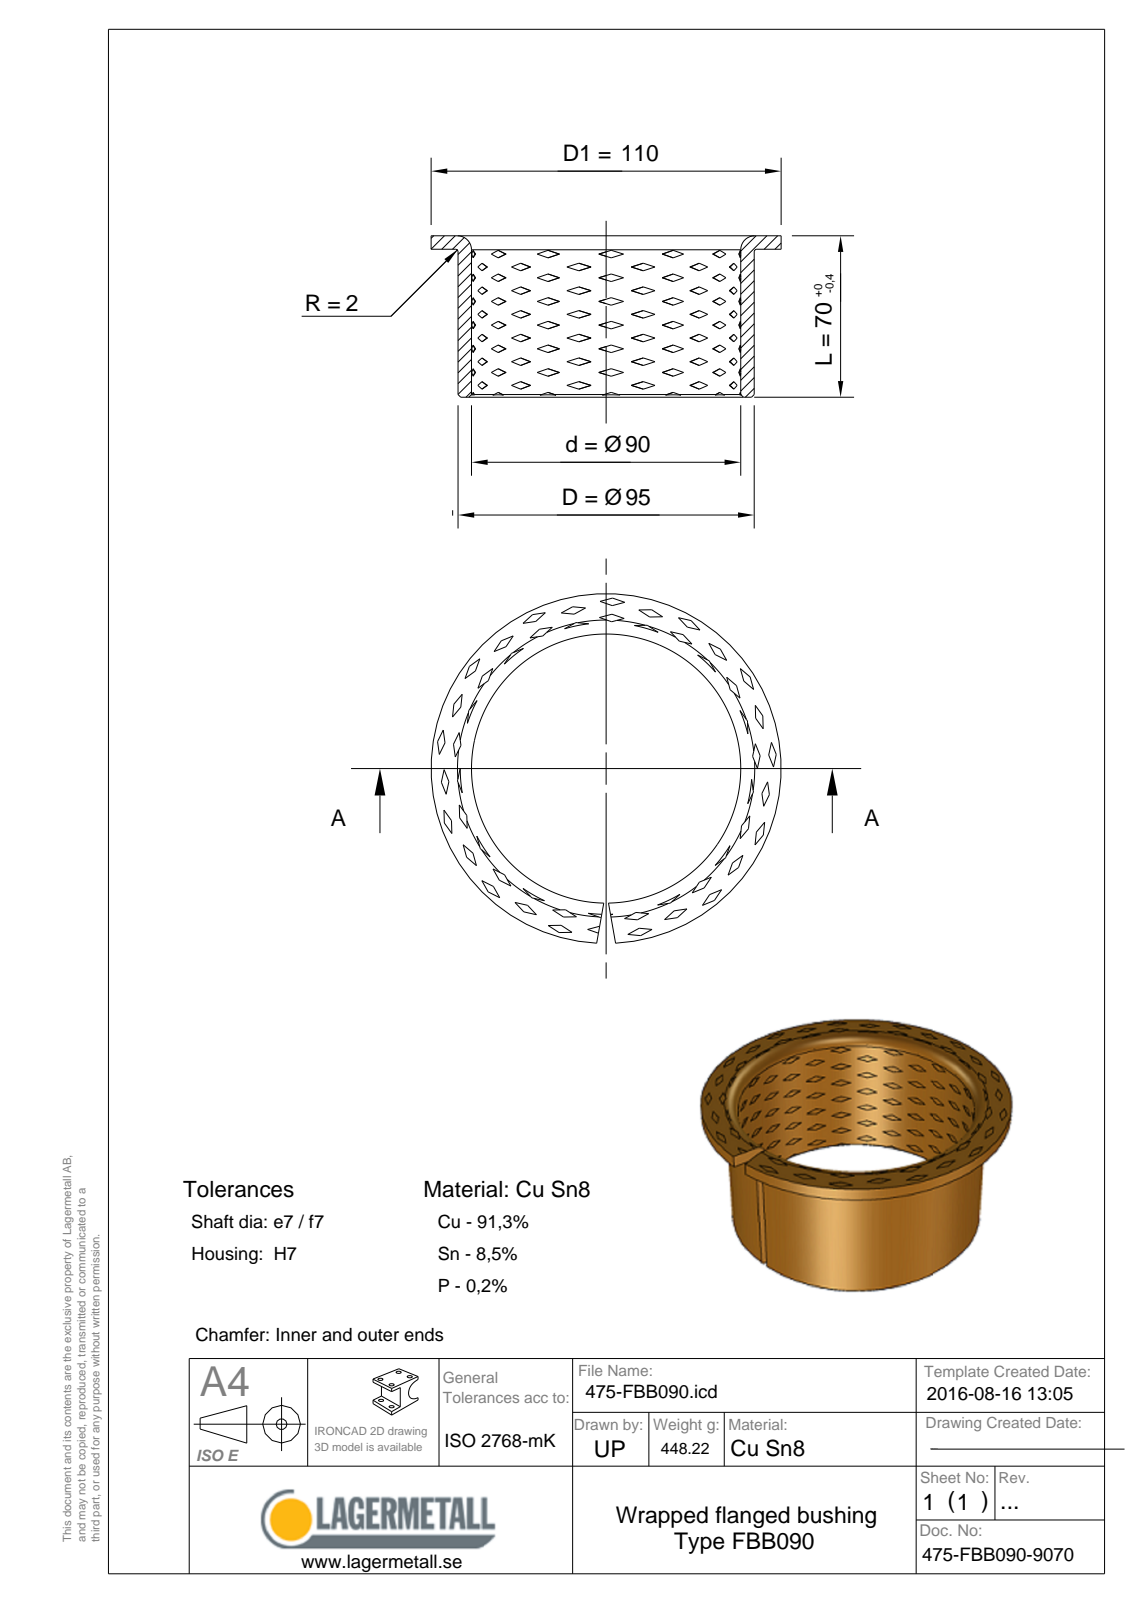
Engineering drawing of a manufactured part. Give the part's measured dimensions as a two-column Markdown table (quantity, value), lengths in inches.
| quantity | value |
| --- | --- |
| part name | 475-FBB090-9070 |
| STEP written by | Spatial InterOp 3D (CONFIG_CONTROL_DESIGN) |
| units | inches |
| bodies | 1 solid, 12 faces (5 planar, 3 cylindrical, 4 other) |
| overall size | 4.331 × 4.329 × 2.756 |
| volume | 3.377 in³ |
| surface area | 71.52 in² |
| round holes (diameter × count) | 3.543 × 1 |
| round bosses / shafts (diameter × count) | 4.331 × 1, 3.74 × 1 |
| main face-to-face distances | 0.098, 2.657, 2.756 |
